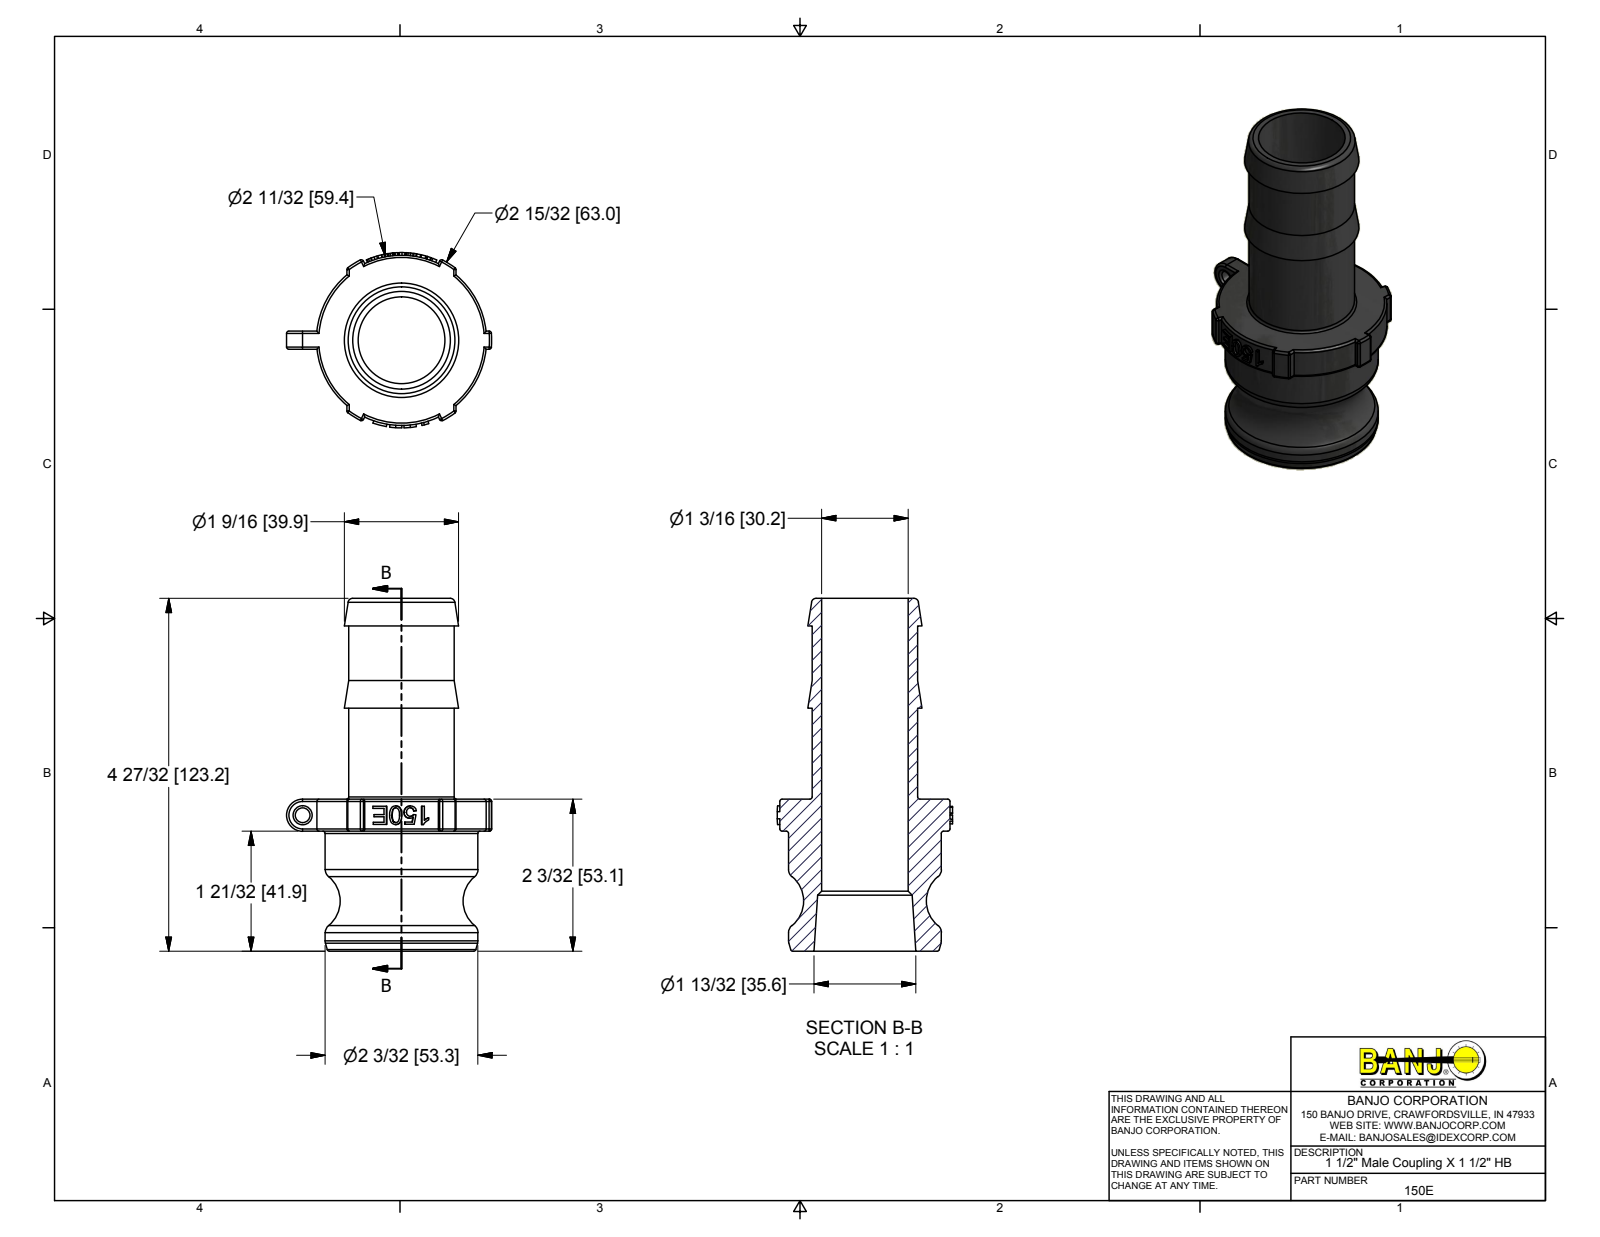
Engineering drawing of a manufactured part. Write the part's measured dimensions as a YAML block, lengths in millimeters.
part_name: "150E"
step_written_by: "Autodesk Inventor 2014 (AUTOMOTIVE_DESIGN)"
units: millimeters
bodies: {solids: 1, faces: 399, planar: 156, cylindrical: 85, other: 158}
overall_size: [123.19, 71.63, 61.21]
volume: 98791
surface_area: 34078
round_holes:
  - {diameter: 5.08, count: 1}
  - {diameter: 30.23, count: 1}
round_bosses_or_shafts:
  - {diameter: 53.34, count: 1}
  - {diameter: 36.83, count: 1}
partial_cylinders:
  - {radius: 0.79, count: 26}
  - {radius: 5.59, count: 1}
  - {radius: 29.72, count: 1}
  - {radius: 30.61, count: 1}
  - {radius: 31.5, count: 1}
face_to_face_distances: [53.09, 41.91, 11.18, 123.19, 81.28, 70.1, 84.84, 113.54, 42.93, 71.63]
